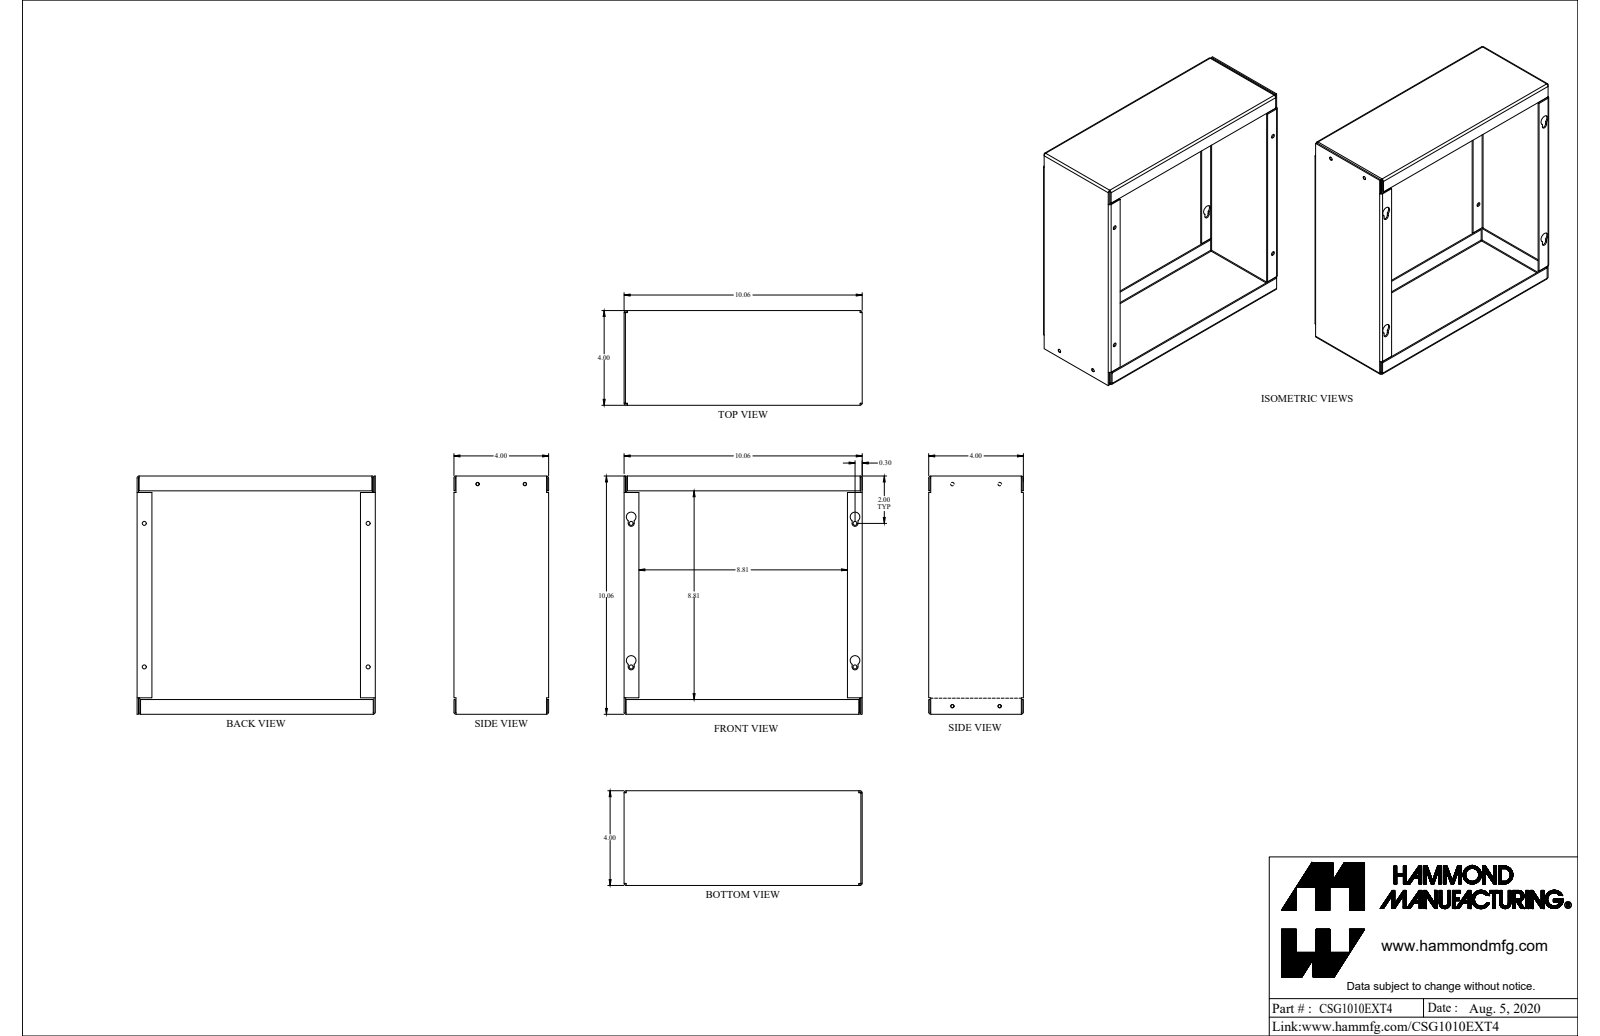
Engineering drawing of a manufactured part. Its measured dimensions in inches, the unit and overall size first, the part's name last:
Units: inches
Overall size (bounding box): 10.063 × 10.063 × 4
Round holes (diameter × count): ⌀0.145 ×4, ⌀0.17 ×4
Round bosses / shafts (diameter × count): ⌀0.131 ×4
Partial cylindrical surfaces — rounded edges, fillets, slot ends (radius × count): R0.029 ×12, R0.086 ×12, R0.125 ×4, R0.203 ×4
Main face-to-face distances: 10.006, 0.057, 0.057, 9.948, 3.943, 10.063, 10.062, 9.949, 3.886, 4
Hole centre spacings: 2, 6.062, 9.38, 9.459, 9.591, 11.235
Volume: 11.59 in³ · Surface area: 413.5 in²
Bodies: 2 solids, 124 faces (80 planar, 44 cylindrical, 0 other)
Part name (STEP PRODUCT): CSG1010EXT4
STEP written by: SolidWorks 2021 (AUTOMOTIVE_DESIGN)
